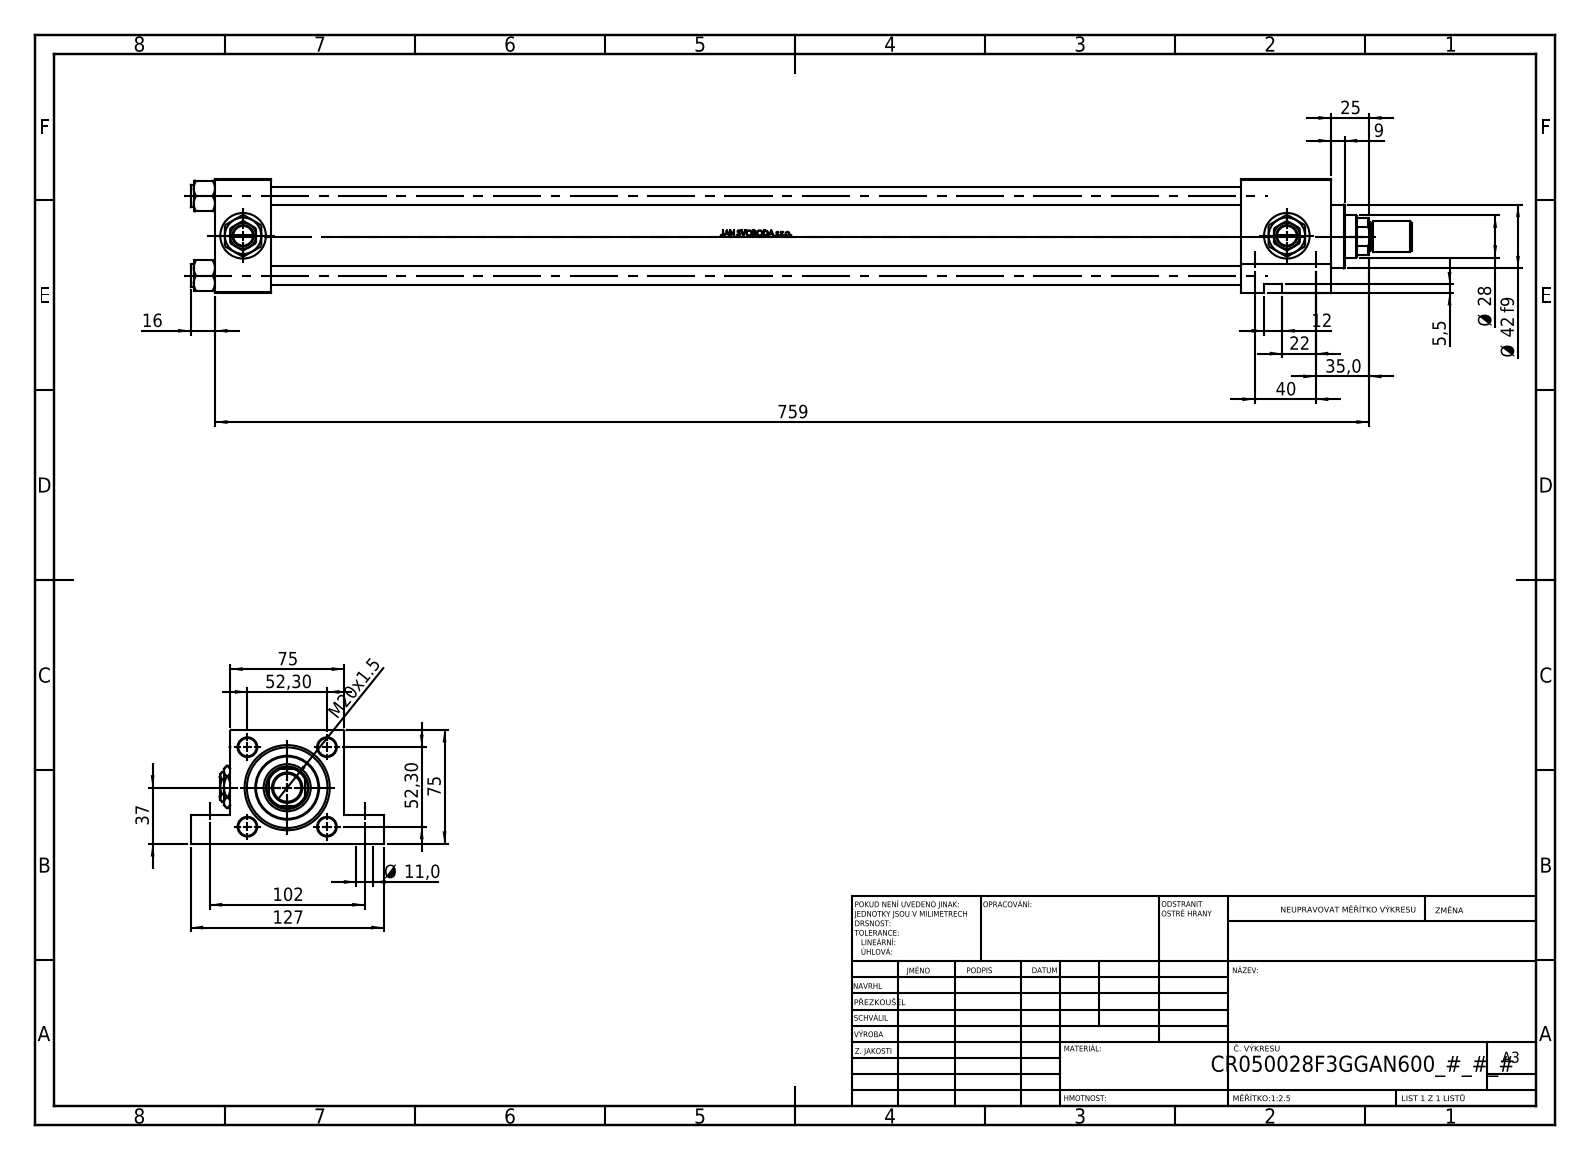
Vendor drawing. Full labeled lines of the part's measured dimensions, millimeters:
Part name (STEP PRODUCT): NUT_M5_F; V215CR_F_TYCINKA; V215CR_VCP_F; Zatka_pro_OIL_PORT (+3 more)
STEP written by: SolidWorks 2019 (CONFIG_CONTROL_DESIGN)
Units: millimetres
Bodies: 14 solids, 1216 faces (488 planar, 140 cylindrical, 588 other)
Overall size (bounding box): 803 × 127 × 75
Volume: 1 631 000 mm³ · Surface area: 498 475 mm²
Round holes (diameter × count): ⌀11 ×4, ⌀12 ×4, ⌀20.96 ×4, ⌀30 ×4, ⌀7 ×3, ⌀18.5 ×1, ⌀28 ×1, ⌀31 ×1, ⌀41 ×1, ⌀50 ×1, ⌀53 ×1
Round bosses / shafts (diameter × count): ⌀15 ×4, ⌀56 ×1, ⌀42 ×1, ⌀20 ×1, ⌀18 ×1
Partial cylindrical surfaces — rounded edges, fillets, slot ends (radius × count): R13.5 ×1
Main face-to-face distances: 75, 37, 734, 697, 675, 638, 59, 19, 56, 74.8
Hole centre spacings: 52.3, 36.63, 37.34, 40, 51.62, 60.21, 73.96, 102
